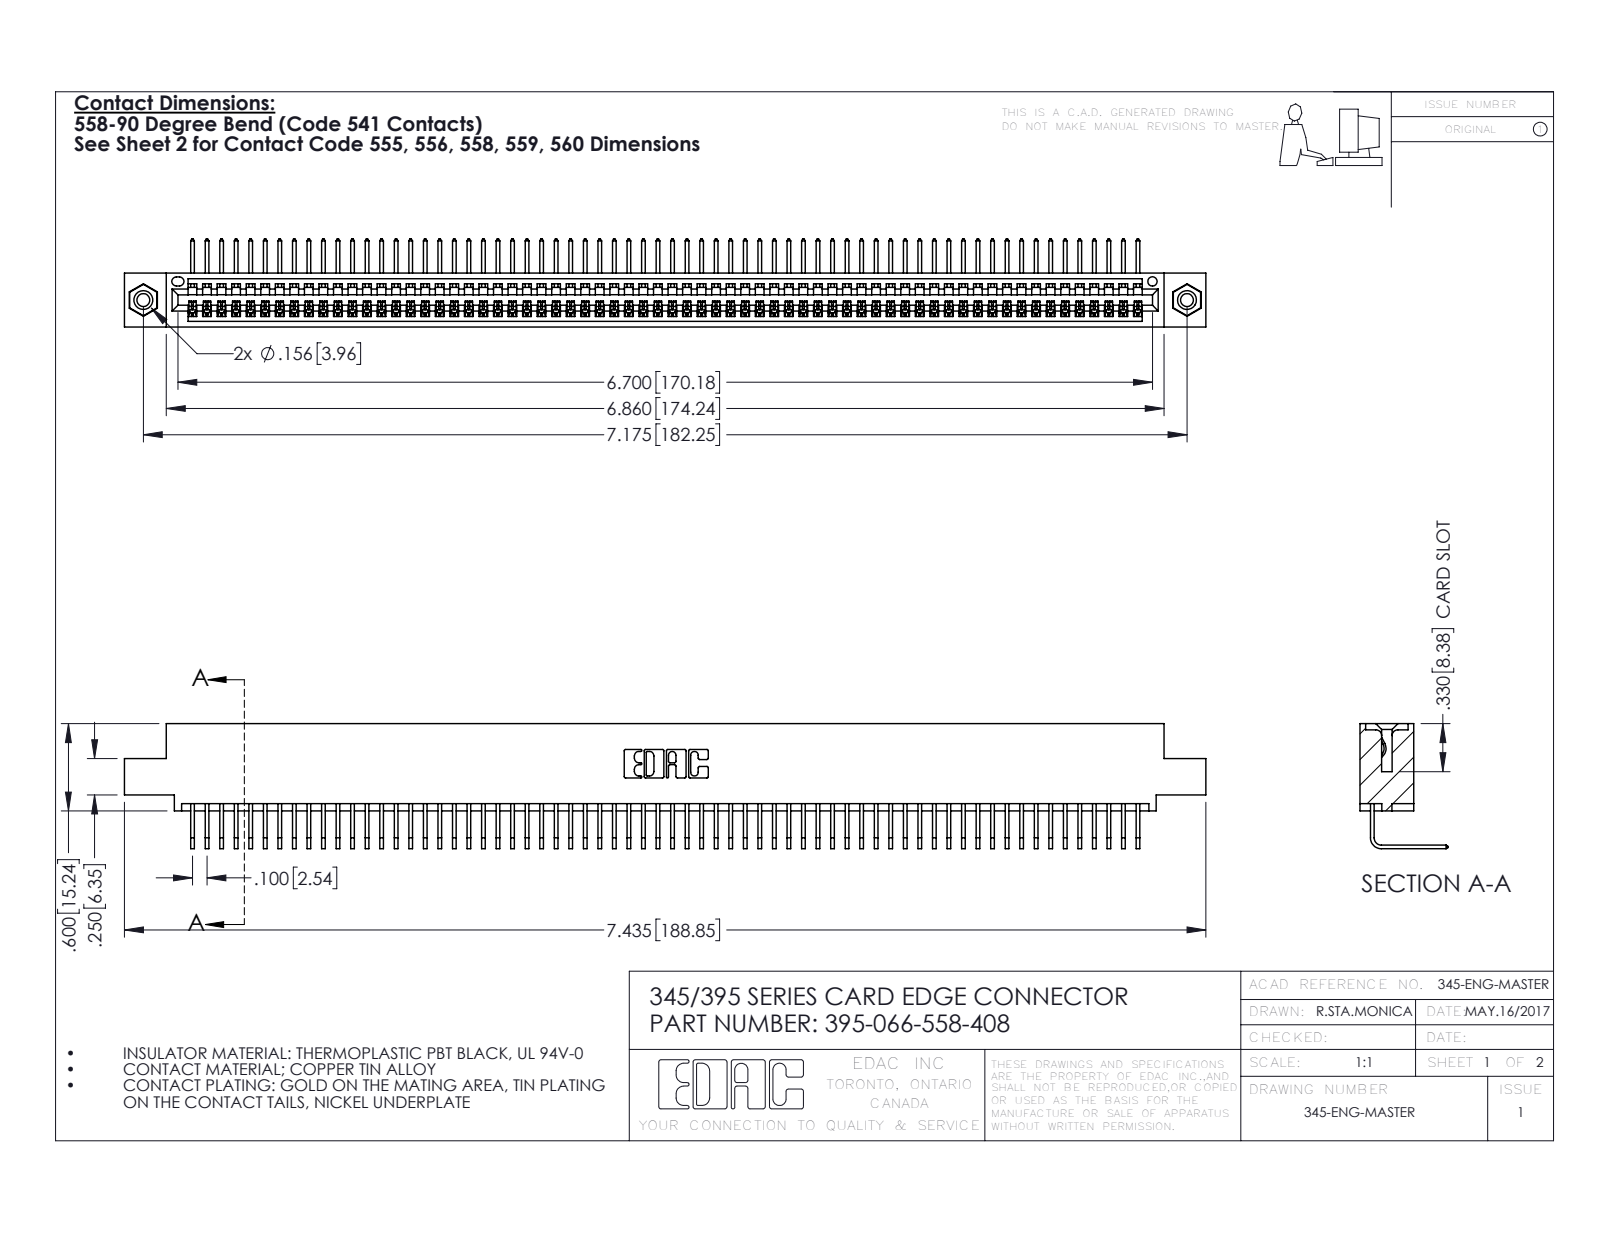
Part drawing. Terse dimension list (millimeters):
name: 345-250-001_345-250-003-102; 345 Part_0.110 Offset - 0.156 Dia-TI; 345-292-001_558 Tail - 2; 395-066-558-408
written by: SolidWorks 2016 (CONFIG_CONTROL_DESIGN)
unit: mm
bodies: 69 solids, 4150 faces (2888 planar, 1246 cylindrical, 16 other)
size: 188.8 × 21.8 × 15.4
volume: 18 270 mm³; area: 26 010 mm²
holes: 2× ⌀2.3, 2× ⌀3.2, 2× ⌀4, 1× ⌀1.6
bosses: 2× ⌀3.9
rounds: 132× R0.2, 22× R0.3, 6× R0.2, 6× R0.8, 3× R0.7, 2× R0.8, 2× R1, 1× R0.4
face distances: 1.8, 7.6, 9.4, 5.1, 2.5, 6.9, 0.6, 5.7, 3.8, 1.8
hole spacings: 6.9, 176.3, 182.2
